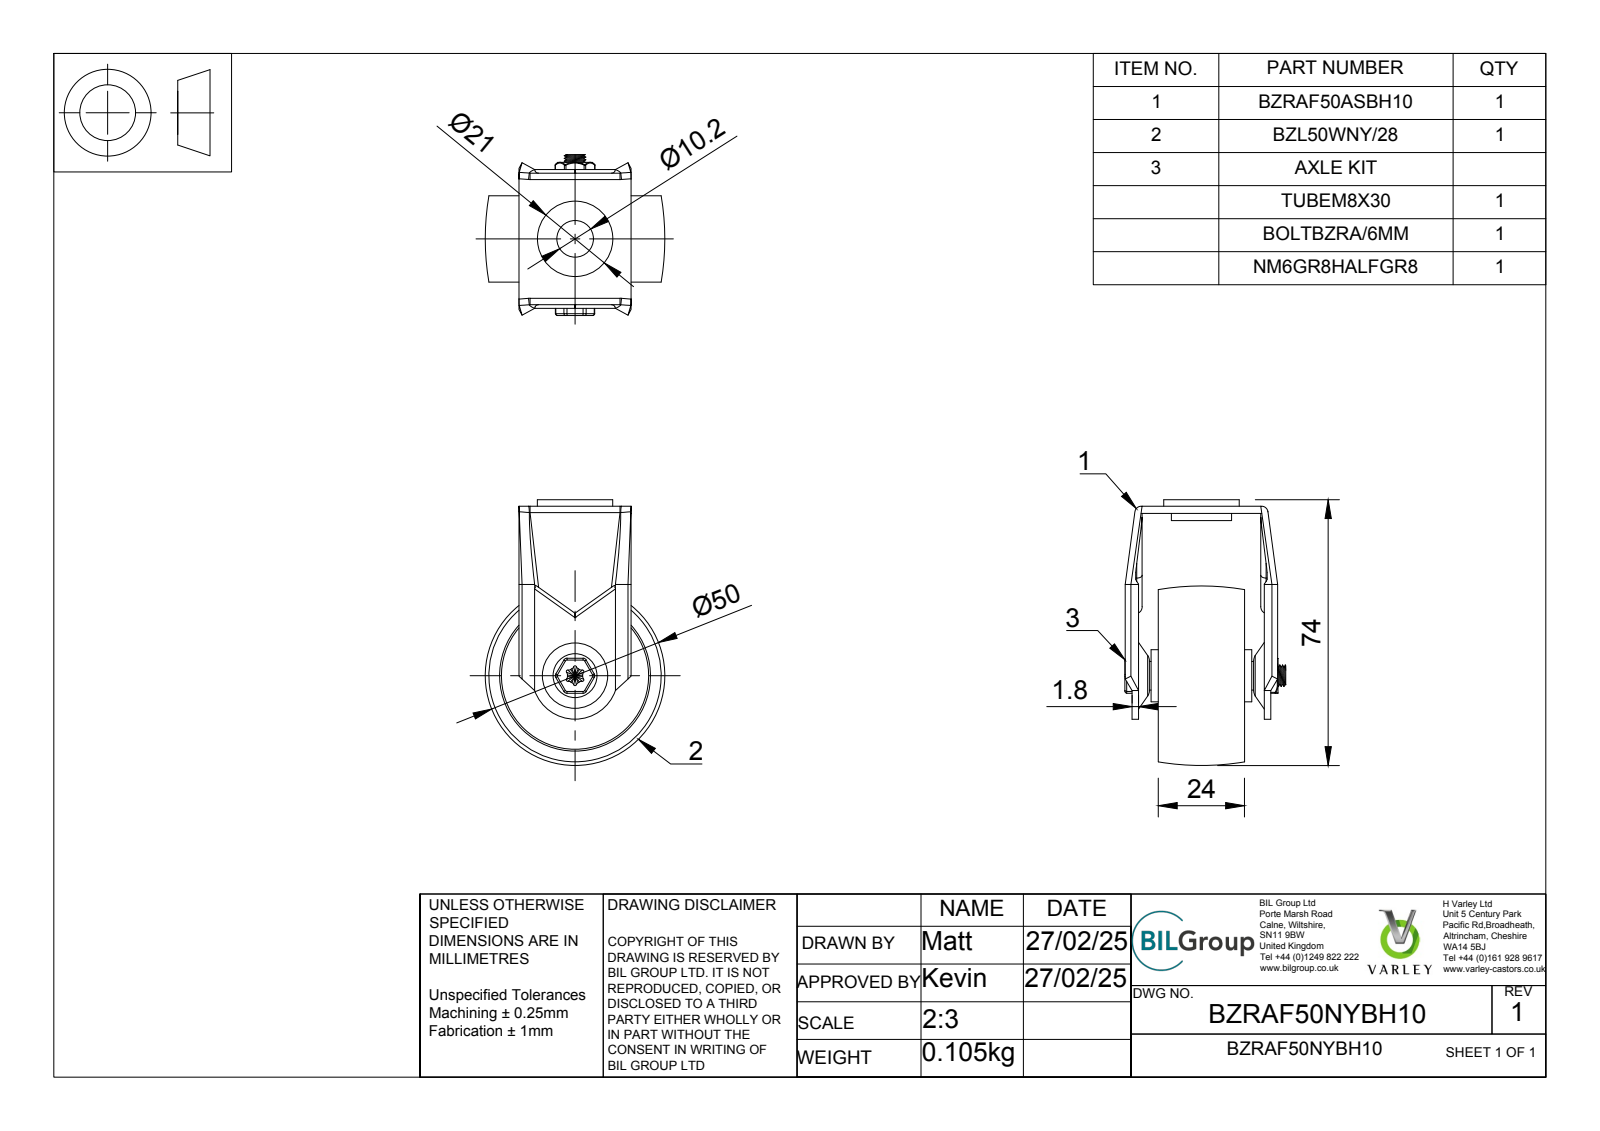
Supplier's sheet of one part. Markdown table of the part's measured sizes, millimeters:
| quantity | value |
| --- | --- |
| part name | BZRAF50NYBH10 v3; BZRAF50ASBH10 v1; ZINC PLATED PRESSED STEEL FORKS; BZL50WNY28 v1 (+7 more) |
| STEP written by | Autodesk Translation Framework v13.20.0.188 (AP242_MANAGED_MODEL_BASED_3D_ENGINEERING_MIM_LF) |
| units | millimeters |
| bodies | 5 solids, 270 faces (74 planar, 92 cylindrical, 104 other) |
| overall size | 74 × 50 × 45 |
| volume | 30 503 mm³ |
| surface area | 24 675 mm² |
| round holes (diameter × count) | 6 × 1, 6.2 × 1, 6.3 × 1, 8.2 × 1, 10.2 × 1, 42 × 1 |
| round bosses / shafts (diameter × count) | 21 × 1, 16.75 × 1, 14.5 × 1, 8 × 1, 7.95 × 1, 5 × 1 |
| partial cylindrical surfaces (radius × count) | 1 × 26, 0.5 × 12, 1.5 × 8, 0.4 × 6, 0.99 × 4, 1.8 × 2, 2.12 × 1, 11.91 × 1 |
| main face-to-face distances | 1.8, 35.8, 1, 3, 2, 19.8, 16.8, 34.8, 15, 18 |
